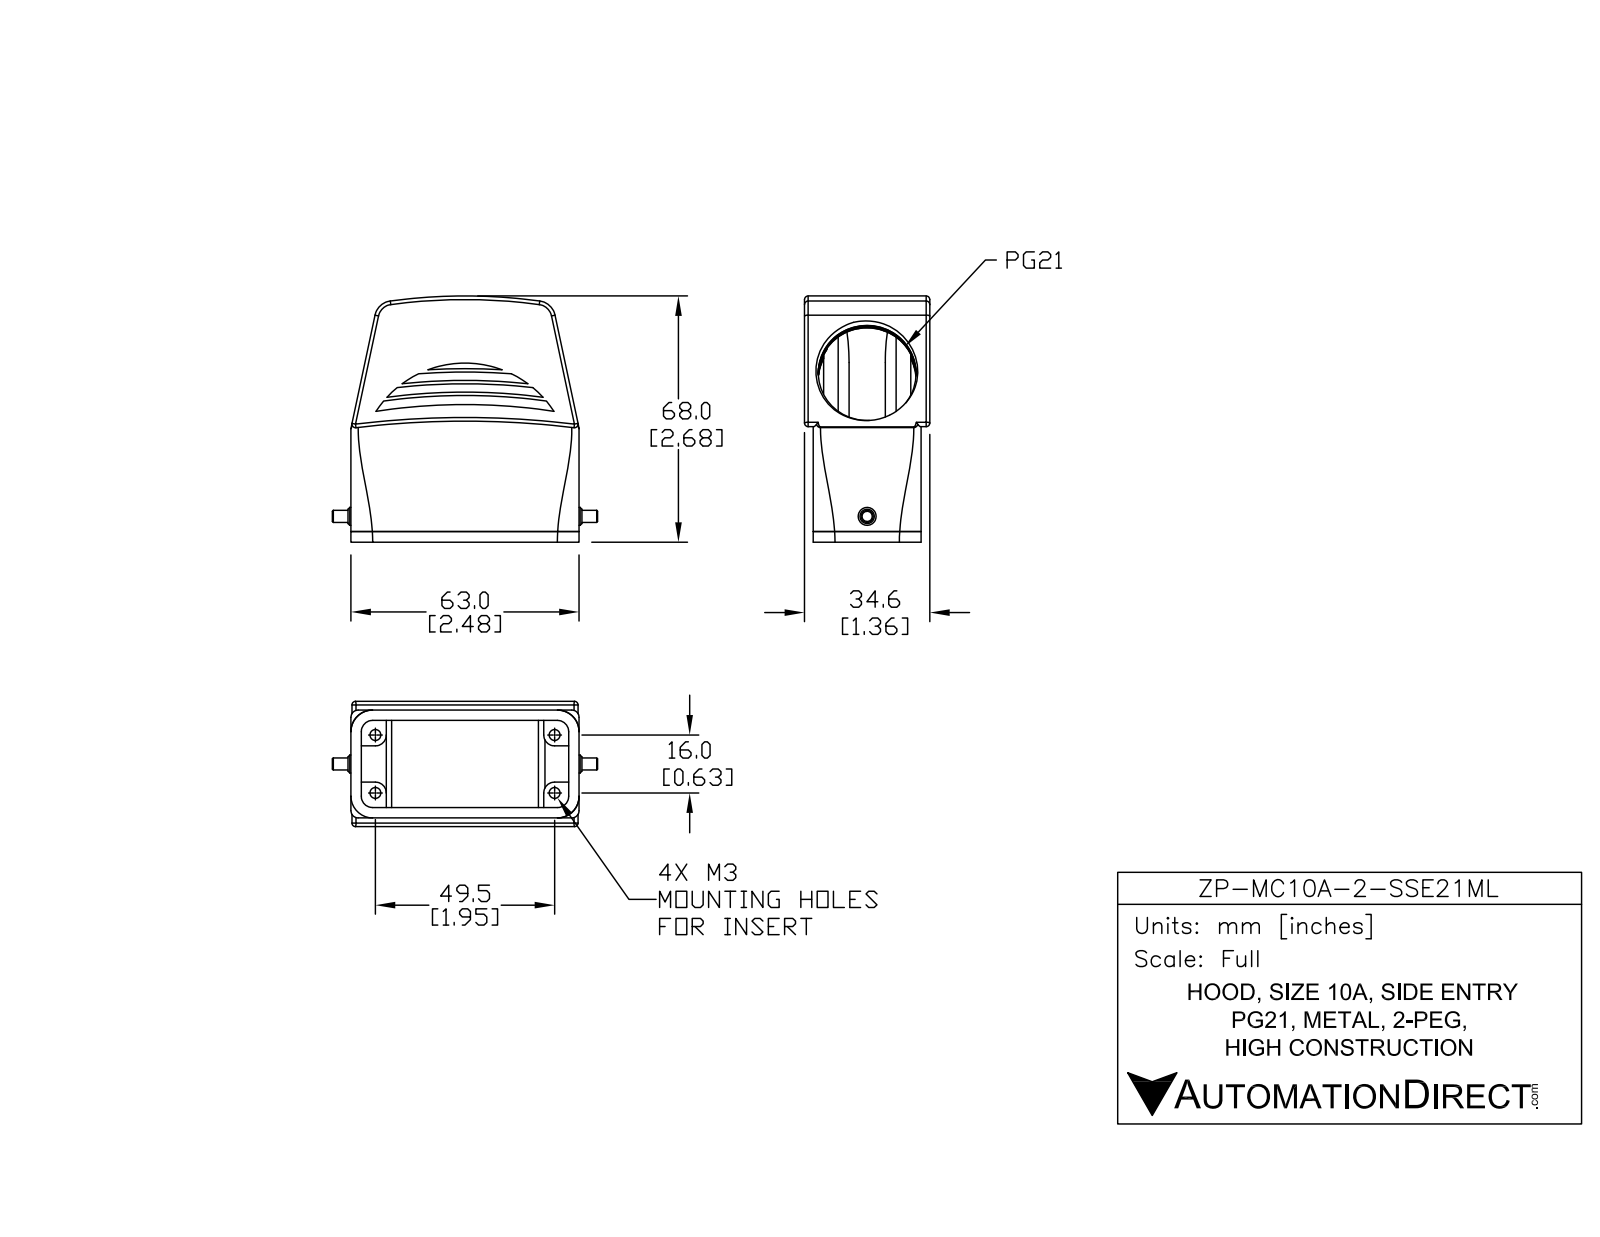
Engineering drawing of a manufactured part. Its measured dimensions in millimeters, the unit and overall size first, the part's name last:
Units: millimetres
Overall size (bounding box): 73.25 × 68 × 34.6
Round holes (diameter × count): ⌀3 ×4, ⌀27 ×1
Round bosses / shafts (diameter × count): ⌀4.95 ×1, ⌀3.33 ×1
Partial cylindrical surfaces — rounded edges, fillets, slot ends (radius × count): R1 ×9, R3 ×4, R2.15 ×2, R5 ×2, R29.32 ×1, R150.6 ×1, R153.45 ×1, R161.93 ×1
Main face-to-face distances: 2.85, 26.93, 24.08, 2.41, 5.26, 29.34, 32.19, 29.78, 34.6, 60.15
Hole centre spacings: 16, 49.5, 52.02
Volume: 46 083 mm³ · Surface area: 26 727 mm²
Bodies: 2 solids, 194 faces (57 planar, 82 cylindrical, 55 other)
Part name (STEP PRODUCT): ZP-MC10A-2-SSE21ML
STEP written by: SolidWorks 2014 (AUTOMOTIVE_DESIGN)
